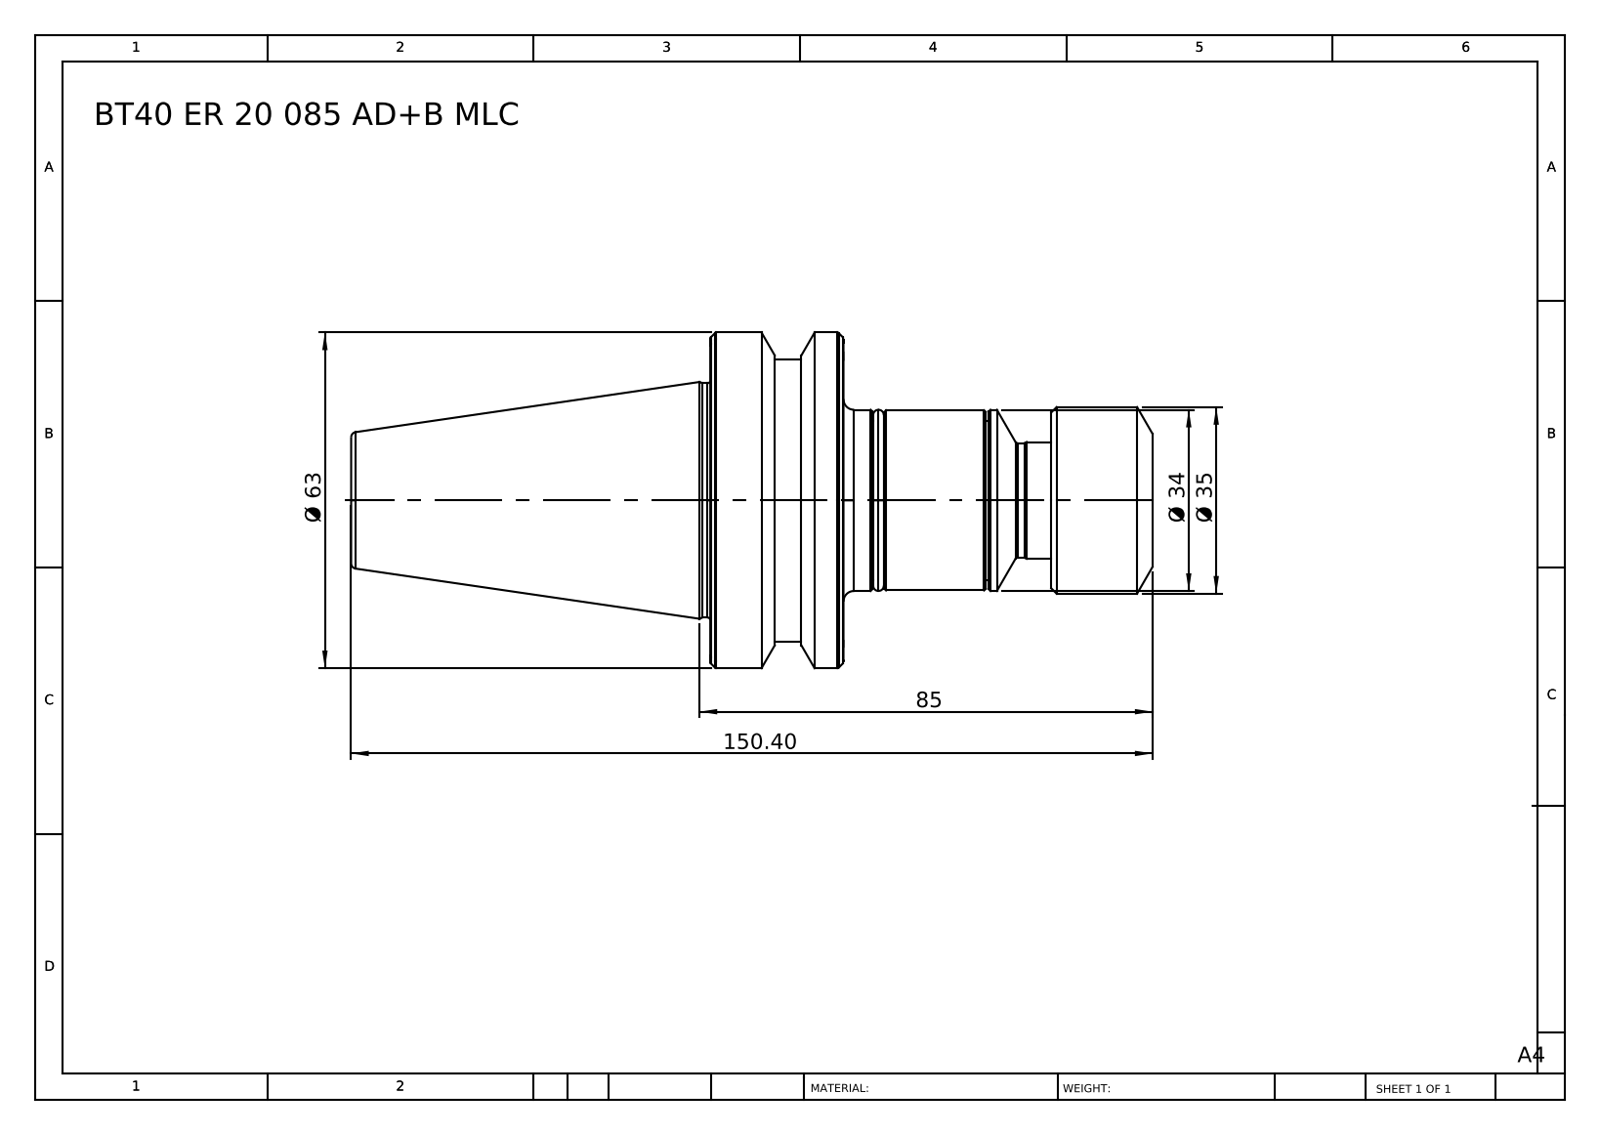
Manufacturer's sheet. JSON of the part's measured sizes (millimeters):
{"part_name": "BT40 ER 20 085 AD+B MLC", "step_written_by": "SolidWorks 2014 (CONFIG_CONTROL_DESIGN)", "units": "millimeters", "bodies": {"solids": 2, "faces": 89, "planar": 11, "cylindrical": 24, "other": 54}, "overall_size": [150.4, 63, 63], "volume_mm3": 186317, "surface_area_mm2": 26118, "round_bosses_or_shafts": [[63, 1], [53, 1], [44, 1], [35, 1], [34, 1], [33.8, 1], [29.9, 1], [21.9, 1]], "face_to_face_distances": [25, 19, 58, 83, 39, 64, 150.4, 131.4, 92.4, 67.4]}
